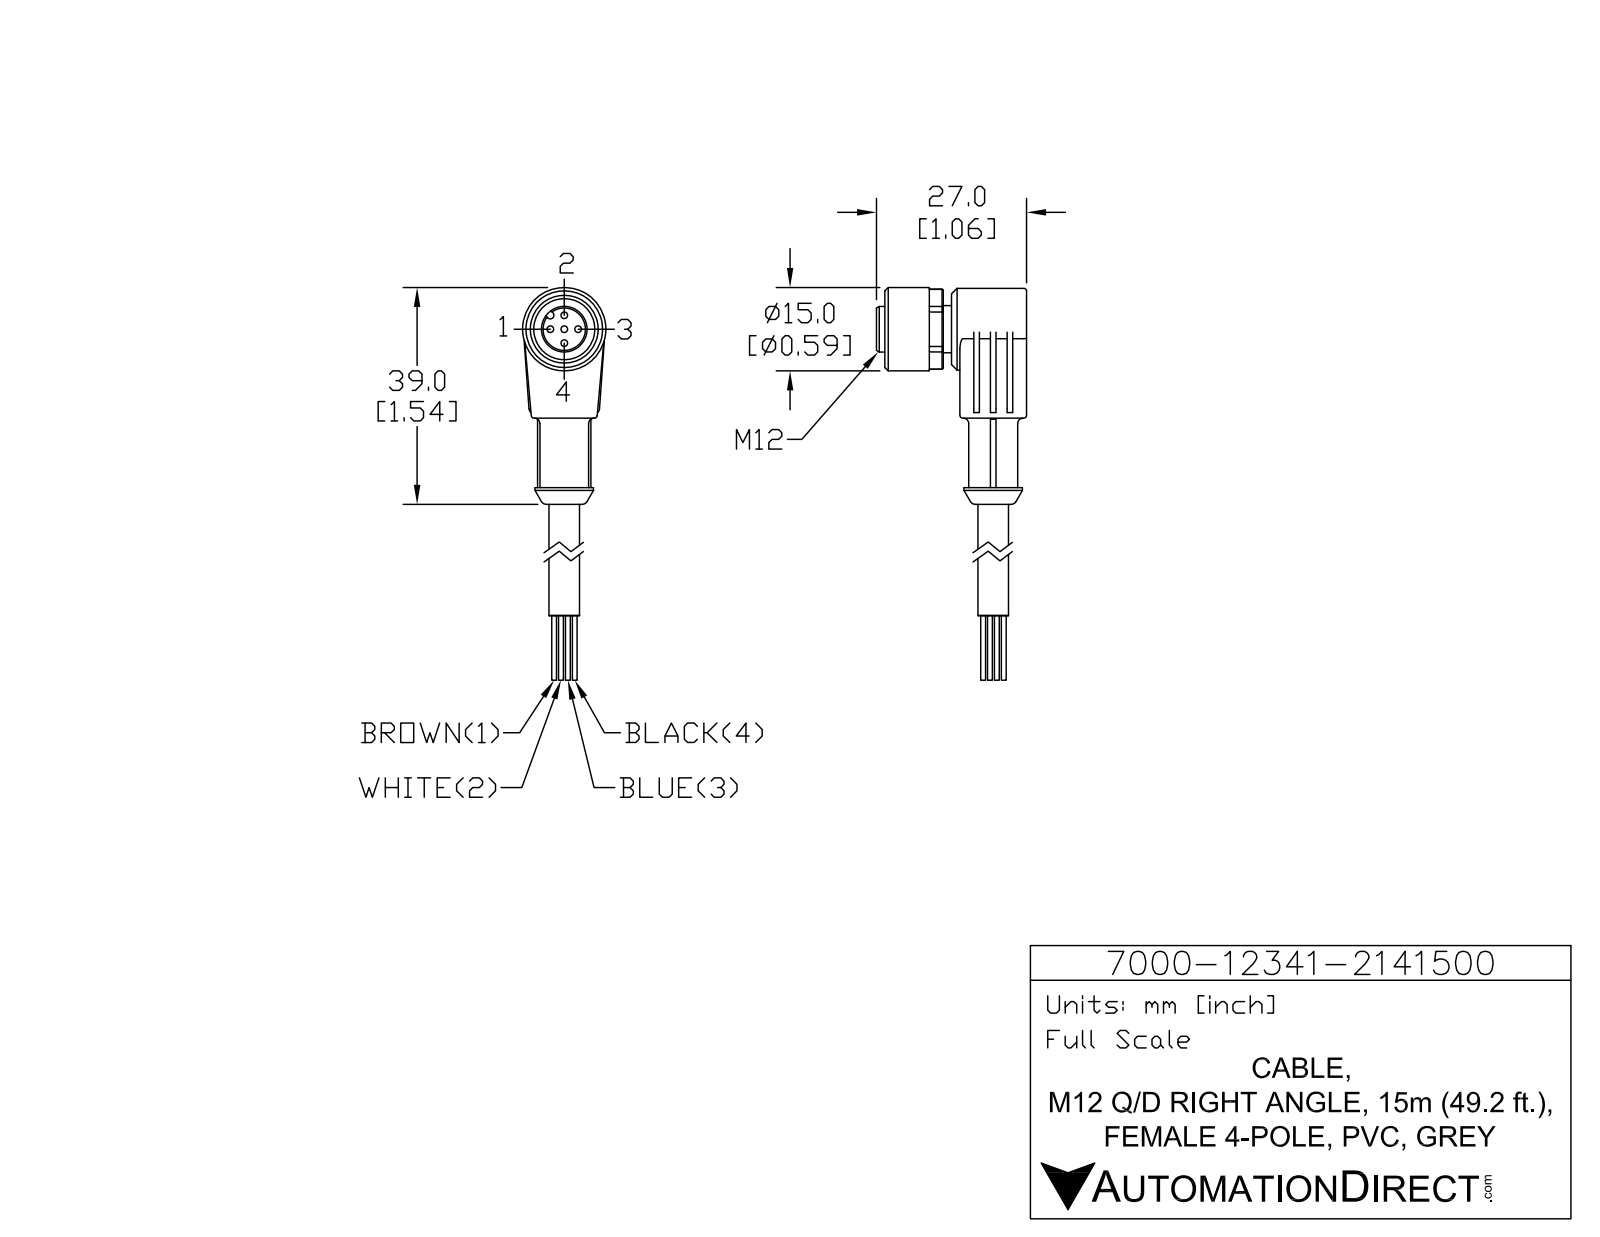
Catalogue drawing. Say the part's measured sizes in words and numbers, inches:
The part is named "7000-12341-2141500". Its 3-D file was written by "SolidWorks 2015 (AUTOMOTIVE_DESIGN)". It is 1 solid with 150 faces: 61 planar, 60 cylindrical and 29 other. Overall it measures 2.323 by 1.063 by 0.591 inches. Its volume is 0.415 cubic inches and its surface area 5.6 square inches. Round holes: 5 of diameter 0.047, 1 of diameter 0.189, 1 of diameter 0.433. Round bosses or shafts: 1 of diameter 0.591, 1 of diameter 0.579, 1 of diameter 0.413, 1 of diameter 0.346, 1 of diameter 0.335, 1 of diameter 0.323, 1 of diameter 0.217. Partial cylindrical surfaces (rounded edges, fillets, slot ends): 8 of radius 0.02, 2 of radius 0.039, 1 of radius 0.026, 1 of radius 0.283. The main face-to-face distances are 0.472, 0.059, 0.118, 0.531, 0.591, 0.217, 0.374, 0.236, 0.315, 0.492. The hole center spacings are 0.098, 0.139, 0.197.
